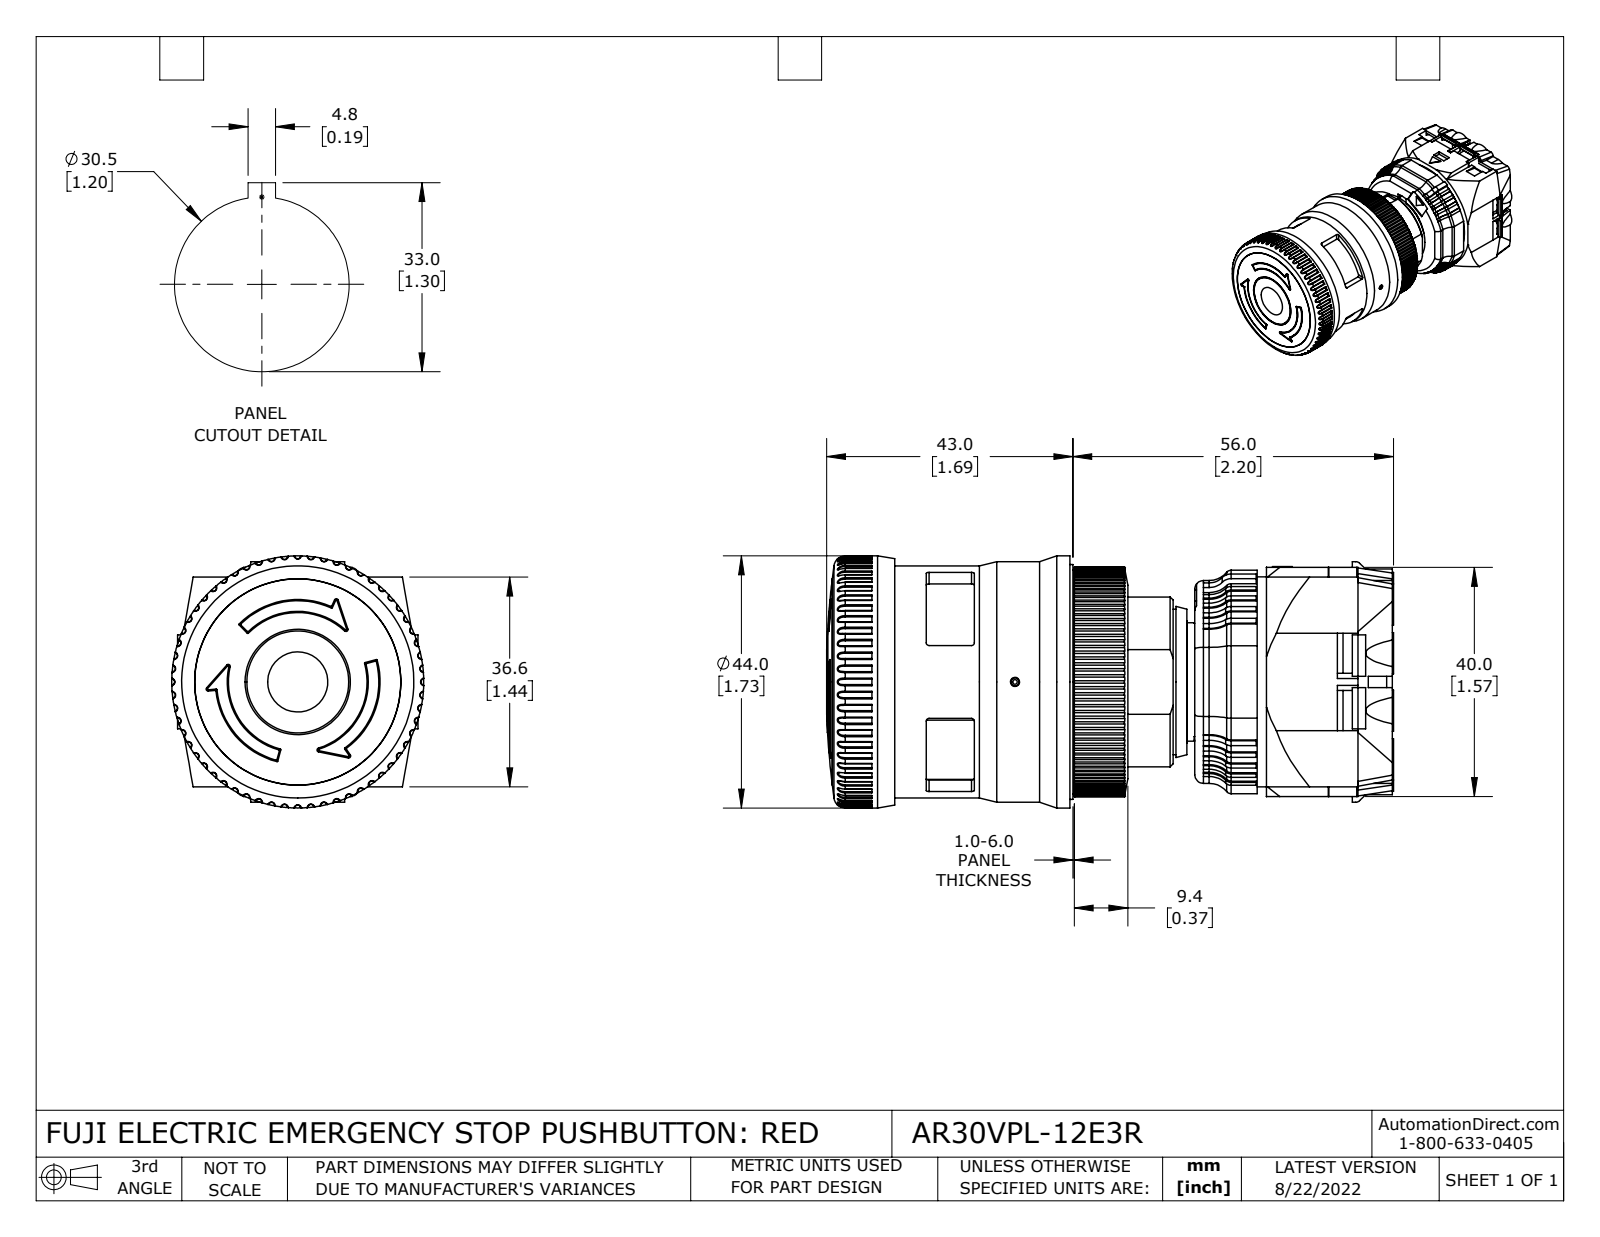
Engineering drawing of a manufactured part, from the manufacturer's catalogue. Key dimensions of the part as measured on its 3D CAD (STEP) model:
Part name (STEP PRODUCT): AR30VPL-12E3R
STEP written by: SolidWorks 2021 (CONFIG_CONTROL_DESIGN)
Units: inches
Bodies: 32 solids, 2480 faces (1039 planar, 1119 cylindrical, 322 other)
Overall size (bounding box): 3.898 × 1.732 × 1.732
Volume: 6.151 in³ · Surface area: 109.1 in²
Round holes (diameter × count): ⌀0.138 ×12, ⌀0.244 ×12, ⌀0.13 ×2, ⌀0.031 ×1, ⌀0.063 ×1, ⌀0.26 ×1, ⌀0.315 ×1, ⌀0.689 ×1, ⌀0.693 ×1, ⌀0.724 ×1, ⌀0.827 ×1, ⌀0.843 ×1
Round bosses / shafts (diameter × count): ⌀0.283 ×12, ⌀1.732 ×1, ⌀1.654 ×1, ⌀1.614 ×1, ⌀1.535 ×1, ⌀1.417 ×1, ⌀1.299 ×1, ⌀1.291 ×1
Partial cylindrical surfaces — rounded edges, fillets, slot ends (radius × count): R0.008 ×120, R0.013 ×120, R0.02 ×76, R0.005 ×24, R0.049 ×19, R0.148 ×19, R0.039 ×15, R0.059 ×12
Main face-to-face distances: 0.118, 1.48, 0.039, 0.839, 1.598, 0.102, 1.516, 1.496, 1.378, 0.339
Hole centre spacings: 0.641, 0.907, 0.325, 0.349, 0.394, 0.585, 0.713, 0.735
